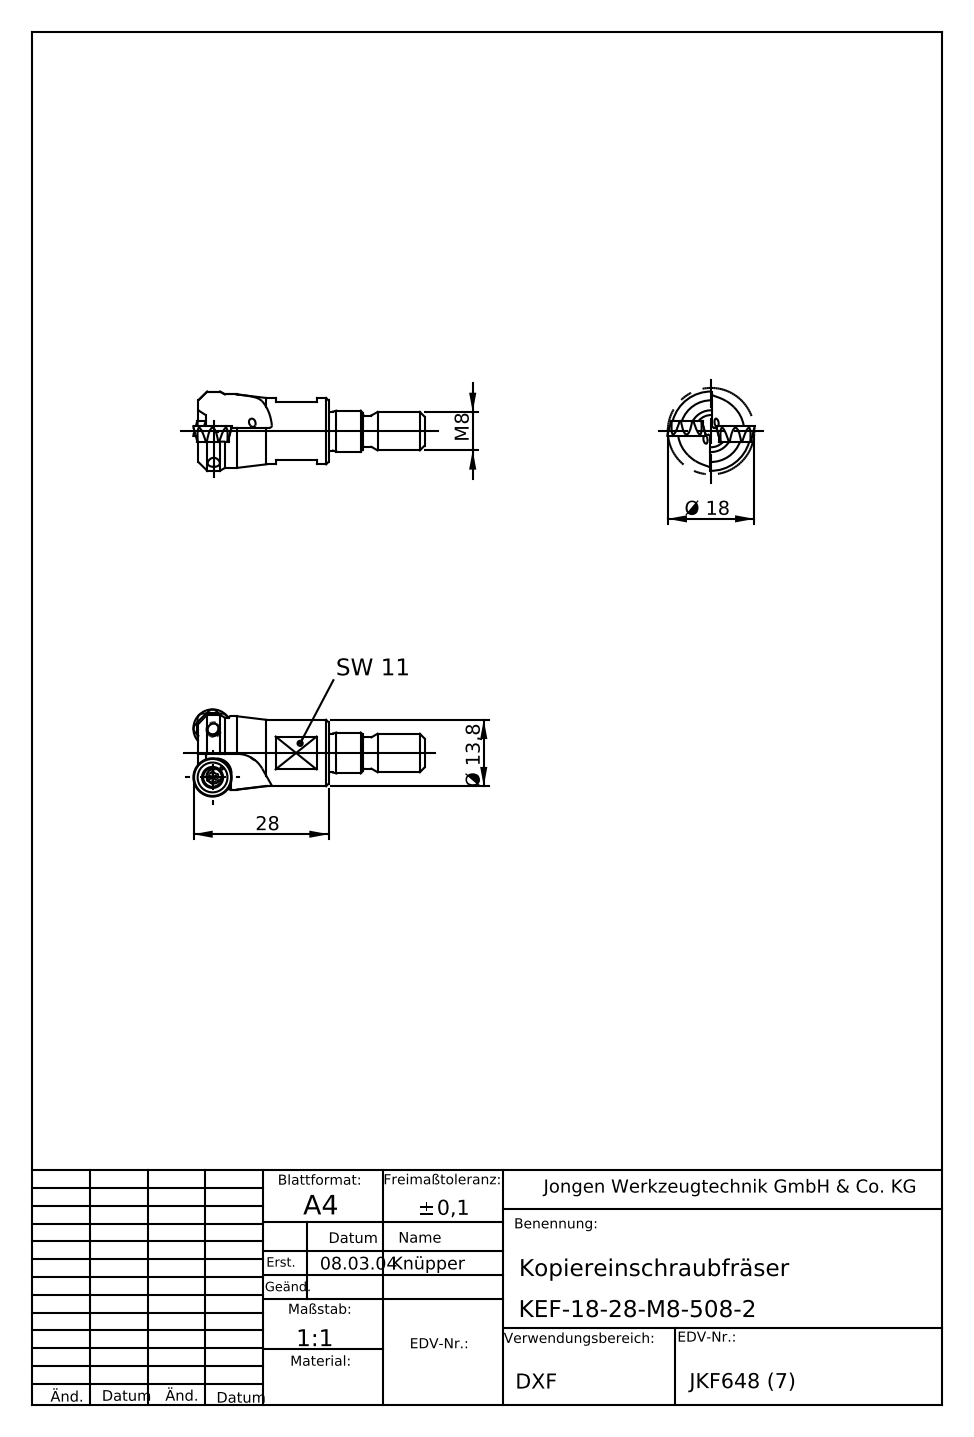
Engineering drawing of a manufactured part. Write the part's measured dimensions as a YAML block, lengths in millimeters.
part_name: "KEF_18_28_M8_508_2"
step_written_by: "SolidWorks 2016 (AUTOMOTIVE_DESIGN)"
units: millimeters
bodies: {solids: 1, faces: 90, planar: 28, cylindrical: 25, other: 37}
overall_size: [47.99, 18, 18]
volume: 5150
surface_area: 2551
round_holes:
  - {diameter: 1.5, count: 2}
  - {diameter: 2, count: 1}
round_bosses_or_shafts:
  - {diameter: 13.8, count: 1}
  - {diameter: 8.5, count: 1}
  - {diameter: 8.1, count: 1}
  - {diameter: 8, count: 1}
  - {diameter: 6.5, count: 1}
partial_cylinders:
  - {radius: 0.5, count: 4}
  - {radius: 6, count: 2}
  - {radius: 7.65, count: 1}
face_to_face_distances: [5.3, 6.7, 12, 1.4, 20, 0.38, 22.5, 2.5, 31, 11]
